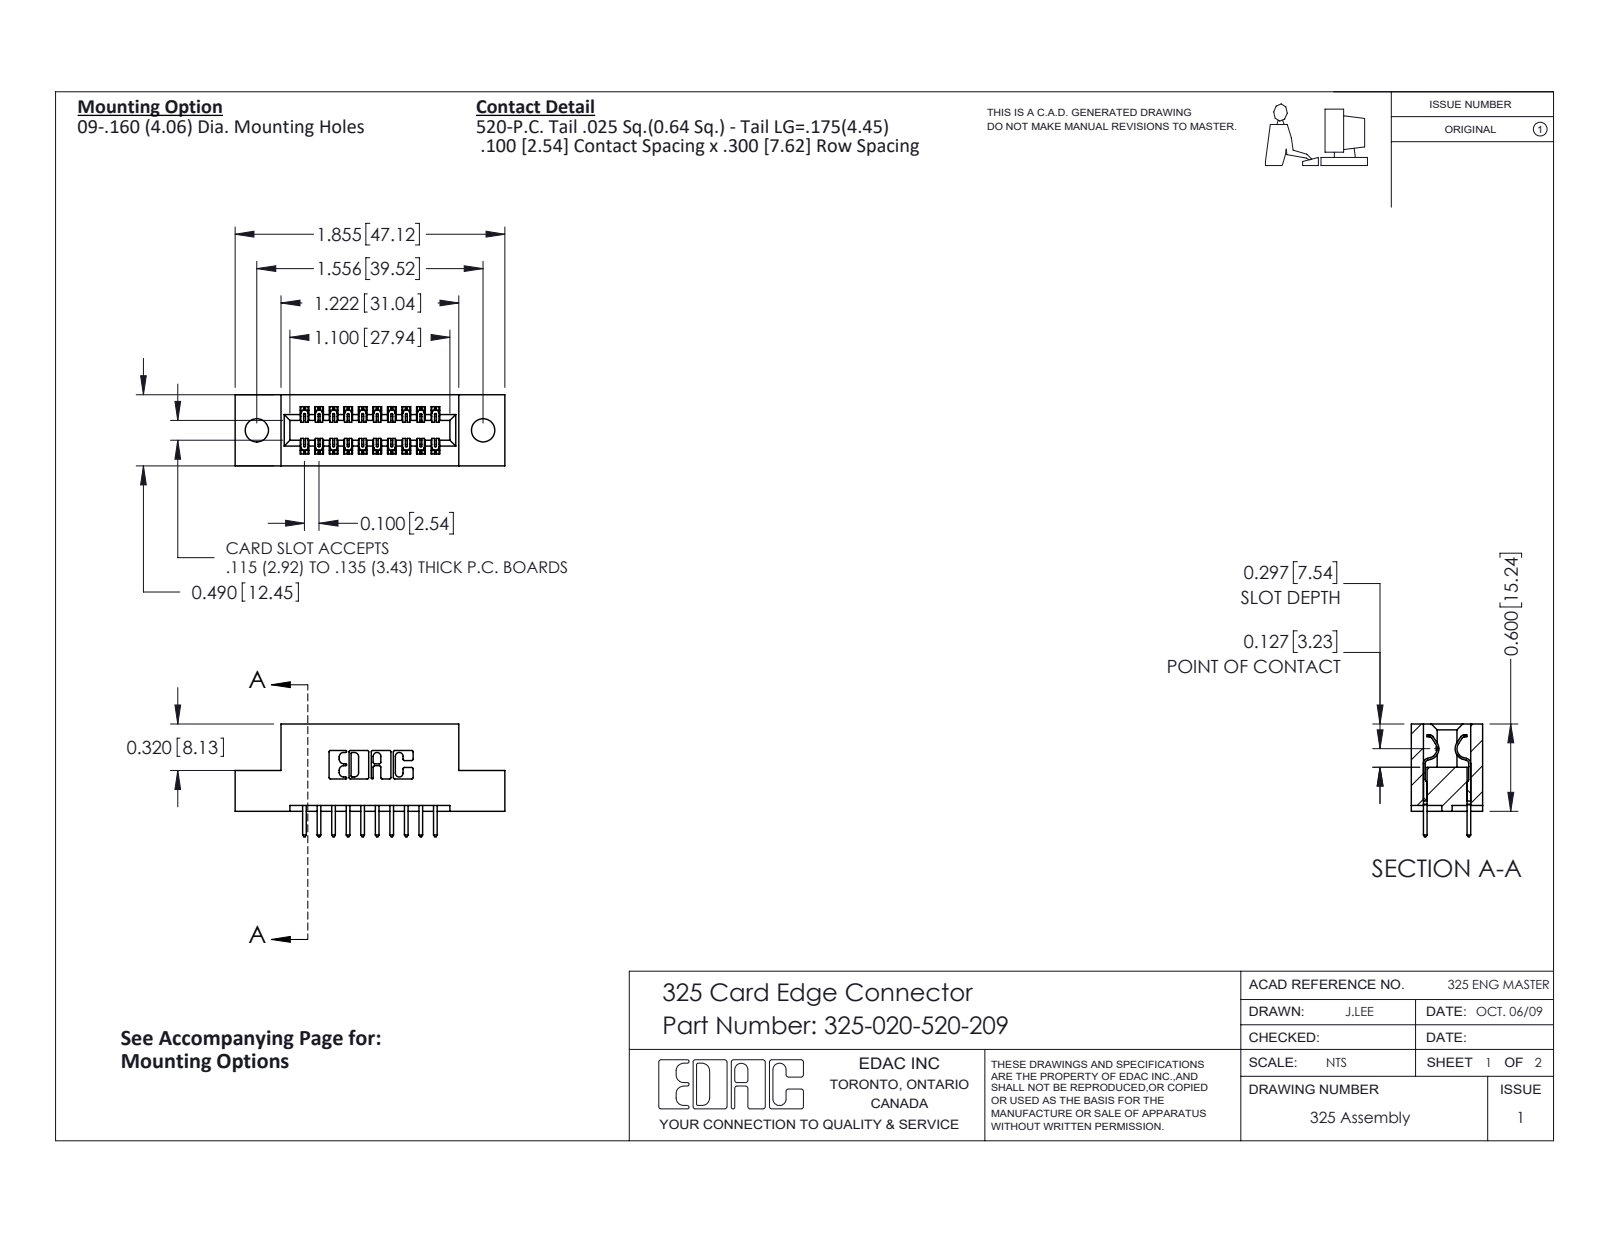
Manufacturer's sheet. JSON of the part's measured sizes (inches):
{"part_name": "325-292-001_325-293-120; 325-020-520-209; 325 Part_.160 TH", "step_written_by": "SolidWorks 2016 (CONFIG_CONTROL_DESIGN)", "units": "inches", "bodies": {"solids": 21, "faces": 1154, "planar": 790, "cylindrical": 364, "other": 0}, "overall_size": [1.855, 0.775, 0.49], "volume_in3": 0.339, "surface_area_in2": 9.072, "round_holes": [[0.16, 2]], "partial_cylinders_radius": [[0.006, 30], [0.01, 22], [0.01, 20], [0.007, 6], [0.031, 6], [0.026, 3], [0.014, 2], [0.022, 2]], "face_to_face_distances": [0.3, 0.083, 0.407, 0.04, 0.1, 0.49, 0.2, 0.107, 0.383, 0.025], "hole_center_spacings": [1.556]}
